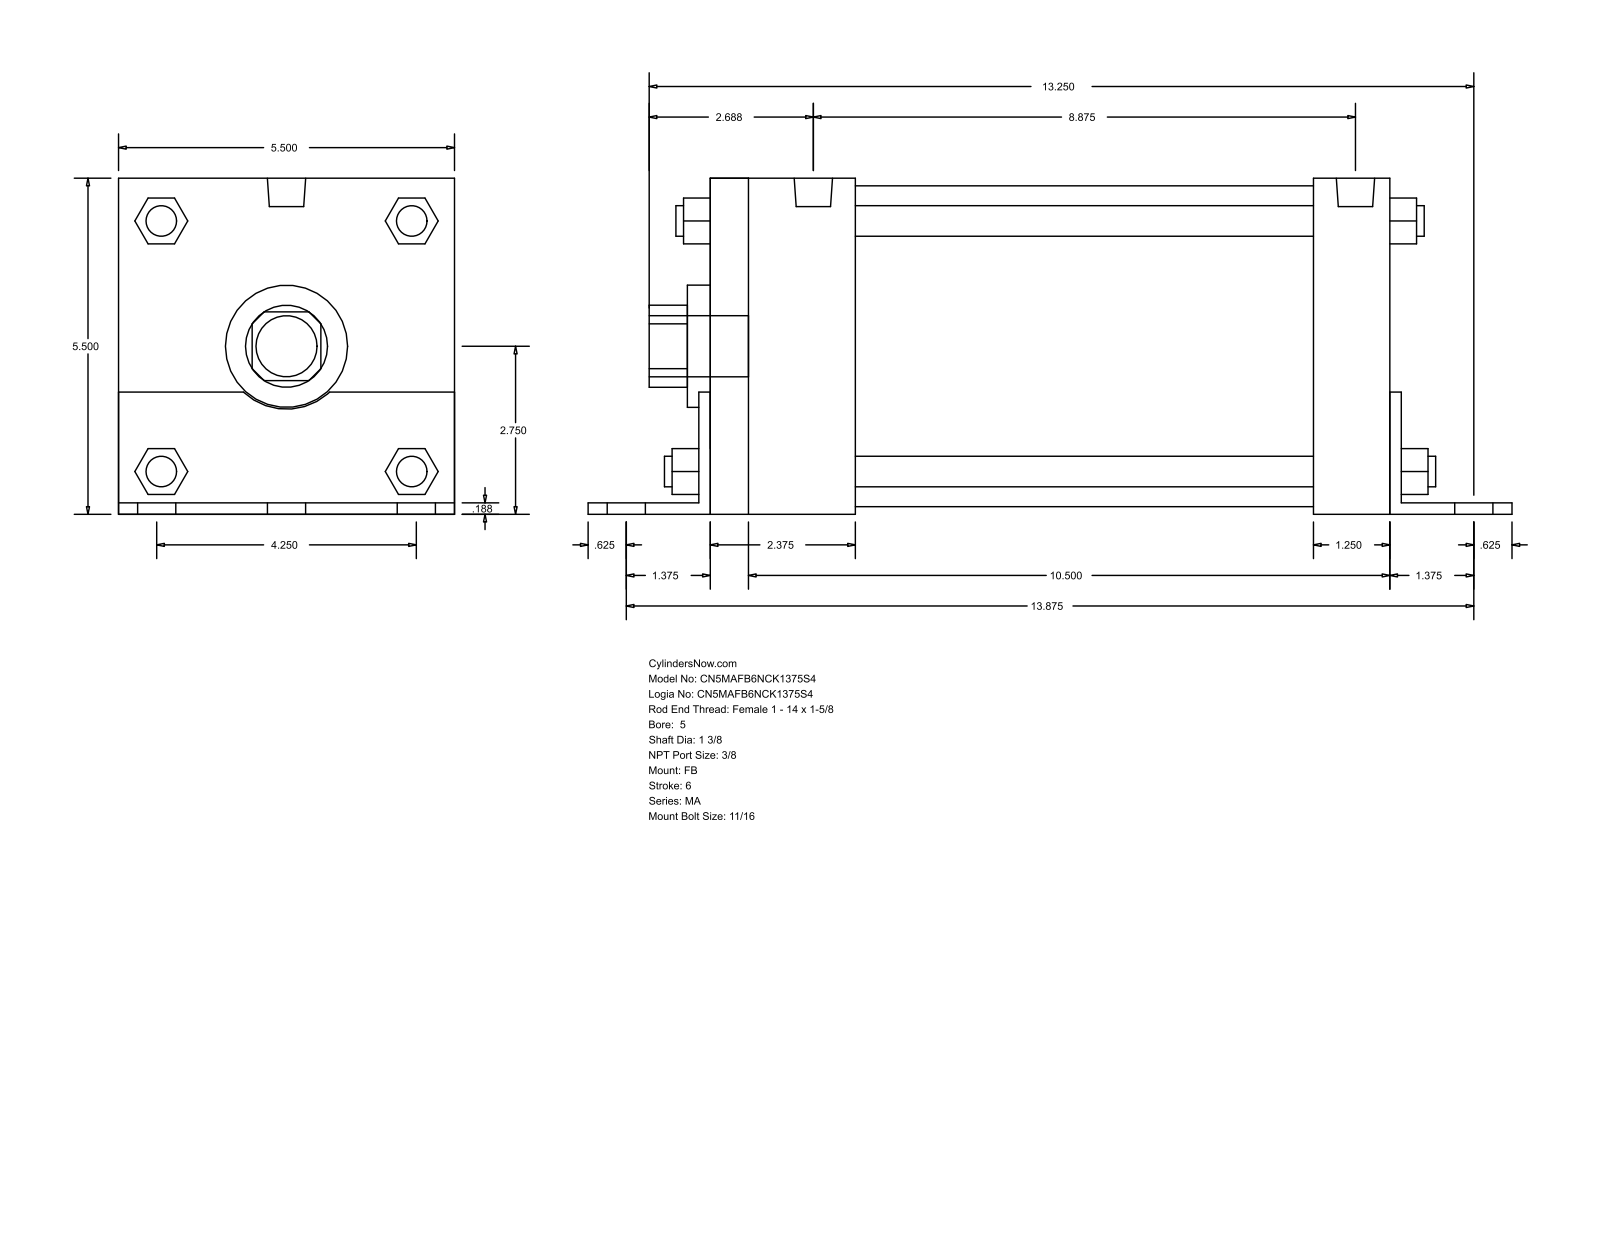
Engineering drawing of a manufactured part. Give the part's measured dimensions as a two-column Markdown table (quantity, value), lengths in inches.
| quantity | value |
| --- | --- |
| part name | MA_FB__0500_1.375 |
| STEP written by | GSSL Pune (CONFIG_CONTROL_DESIGN) |
| units | inches |
| bodies | 0 solids, 140 faces (105 planar, 35 cylindrical, 0 other) |
| overall size | 15.125 × 5.502 × 5.5 |
| round holes (diameter × count) | 1.375 × 1, 2 × 1, 5.25 × 1 |
| round bosses / shafts (diameter × count) | 0.687 × 6, 0.5 × 4, 0.437 × 4, 0.627 × 2, 1 × 1 |
| partial cylindrical surfaces (radius × count) | 0.672 × 1, 1.03 × 1 |
| main face-to-face distances | 5.5, 0.187, 5.502, 11.313, 0.185, 5.315, 11.125, 11.5, 1.25, 1.437 |
